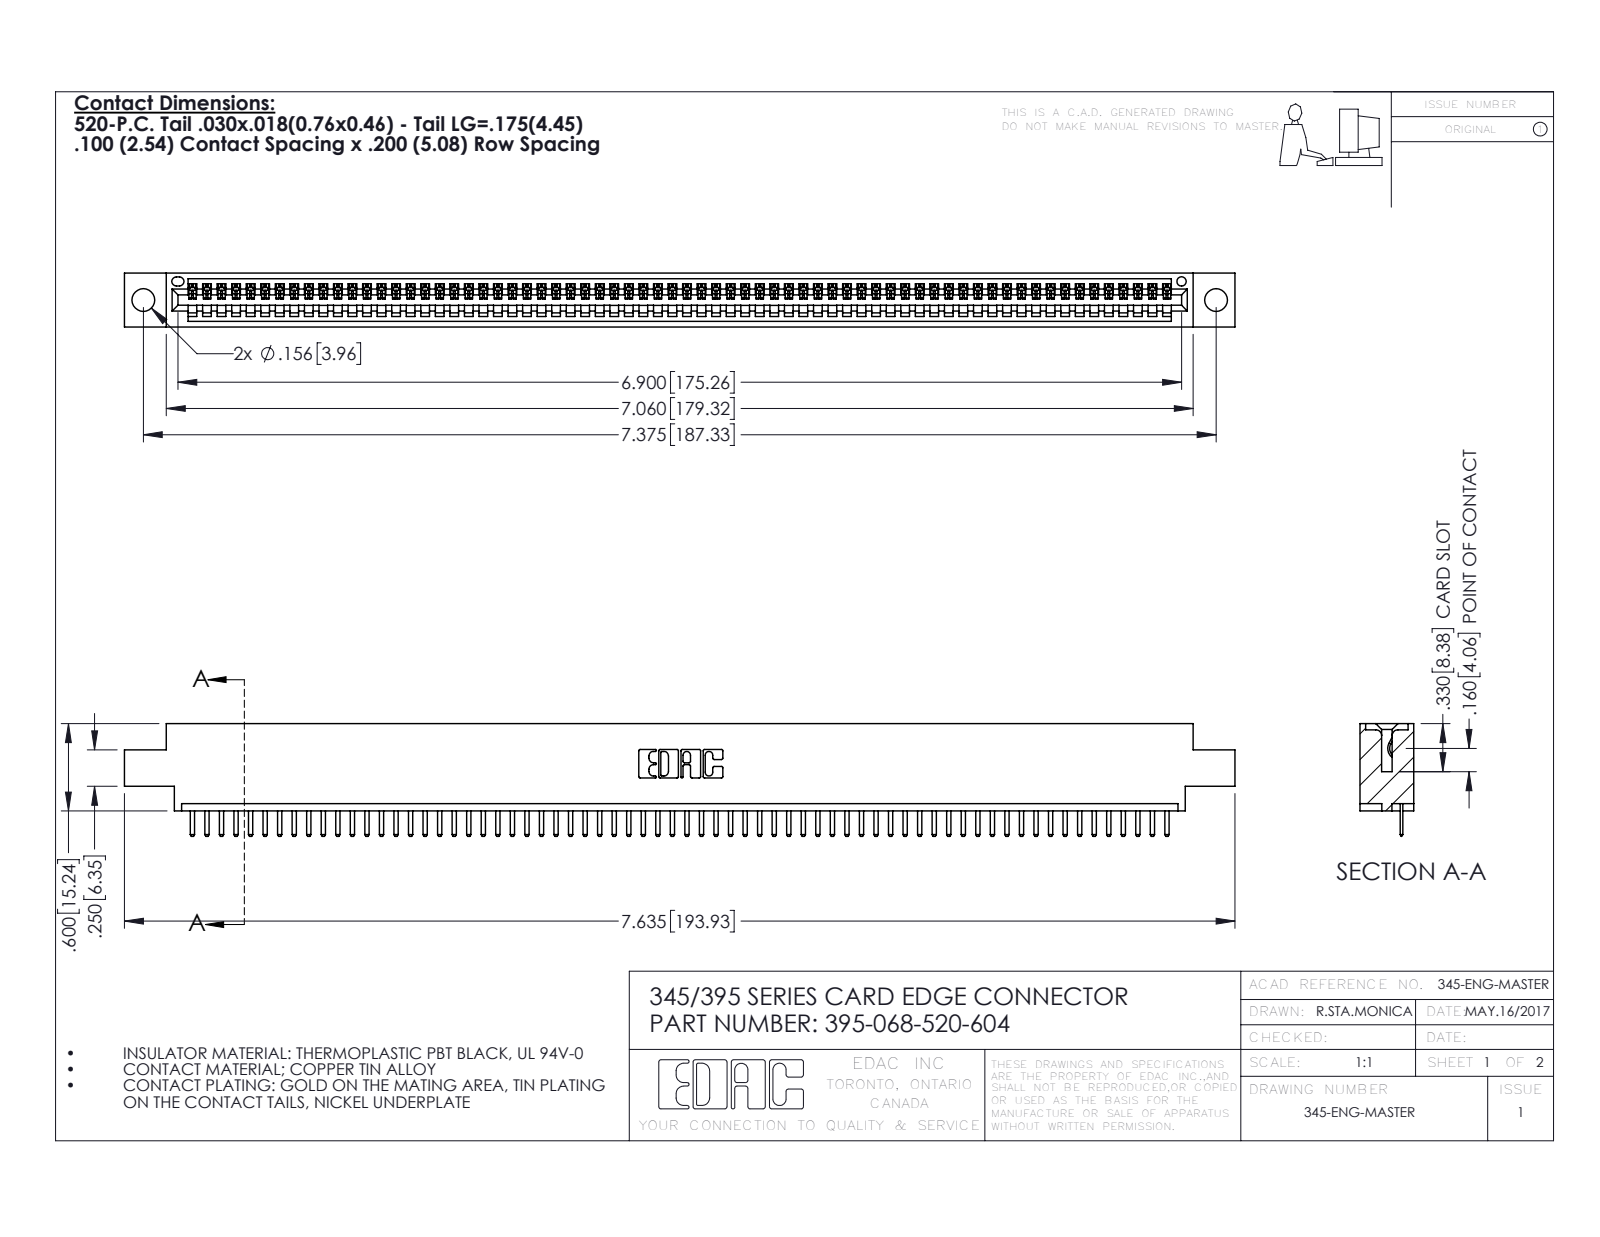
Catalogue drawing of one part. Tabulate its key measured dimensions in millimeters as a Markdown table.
| quantity | value |
| --- | --- |
| part name | 395-068-520-604; 345 Part_0.170 Offset - 0.156 Dia-TH; 345-292-001_345-293-120 |
| STEP written by | SolidWorks 2016 (CONFIG_CONTROL_DESIGN) |
| units | millimeters |
| bodies | 69 solids, 4346 faces (2940 planar, 1406 cylindrical, 0 other) |
| overall size | 193.9 × 19.7 × 9.4 |
| volume | 18 240 mm³ |
| surface area | 23 880 mm² |
| round holes (diameter × count) | 4 × 2, 1.6 × 1 |
| partial cylindrical surfaces (radius × count) | 0.3 × 138, 0.2 × 136, 0.3 × 22, 0.2 × 6, 0.8 × 6, 0.7 × 3, 0.8 × 2, 1 × 2 |
| main face-to-face distances | 7.6, 1.8, 9.4, 5.1, 2.5, 6.9, 0.6, 5.7, 1.8, 4.4 |
| hole center spacings | 6.9, 181.3, 187.3 |
